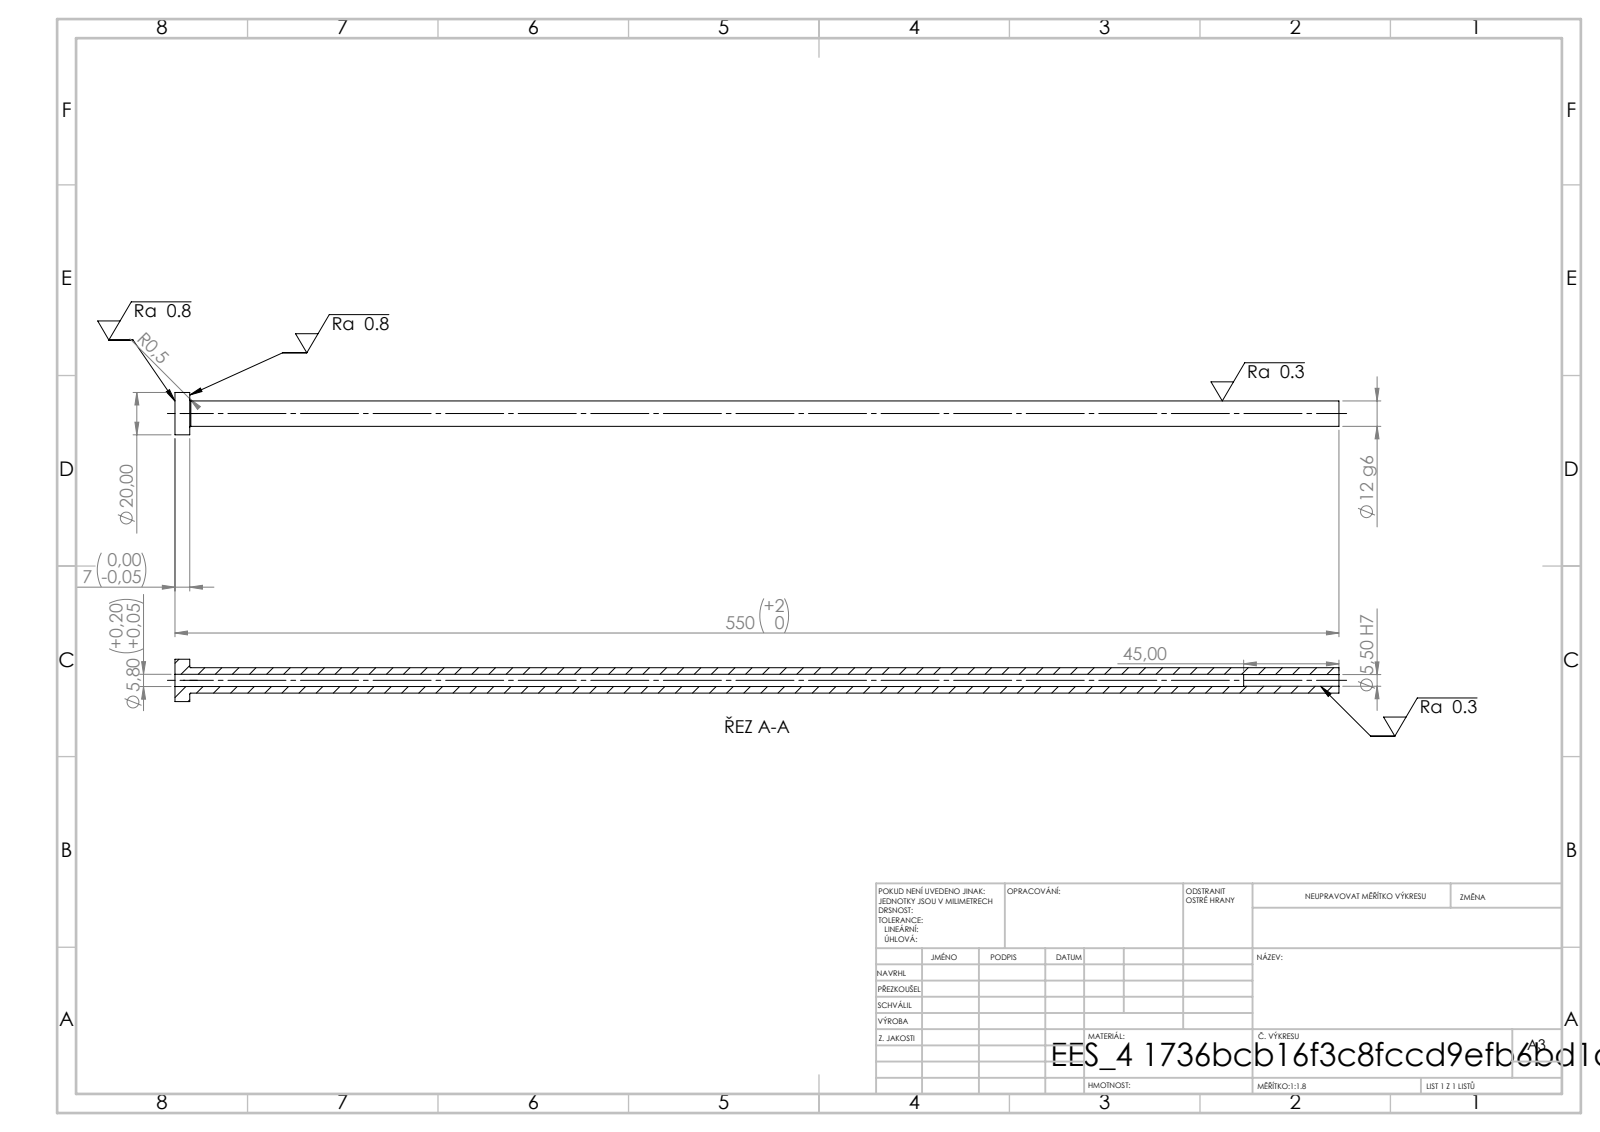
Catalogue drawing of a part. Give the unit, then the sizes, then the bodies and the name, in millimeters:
Units: millimetres
Overall size (bounding box): 550 × 20 × 20
Round holes (diameter × count): ⌀5.5 ×1, ⌀5.8 ×1
Round bosses / shafts (diameter × count): ⌀20 ×1, ⌀12 ×1
Main face-to-face distances: 7, 550, 543, 505, 498, 45
Volume: 49 201 mm³ · Surface area: 31 463 mm²
Bodies: 1 solid, 14 faces (4 planar, 8 cylindrical, 2 other)
STEP written by: SolidWorks 2019 (CONFIG_CONTROL_DESIGN)
